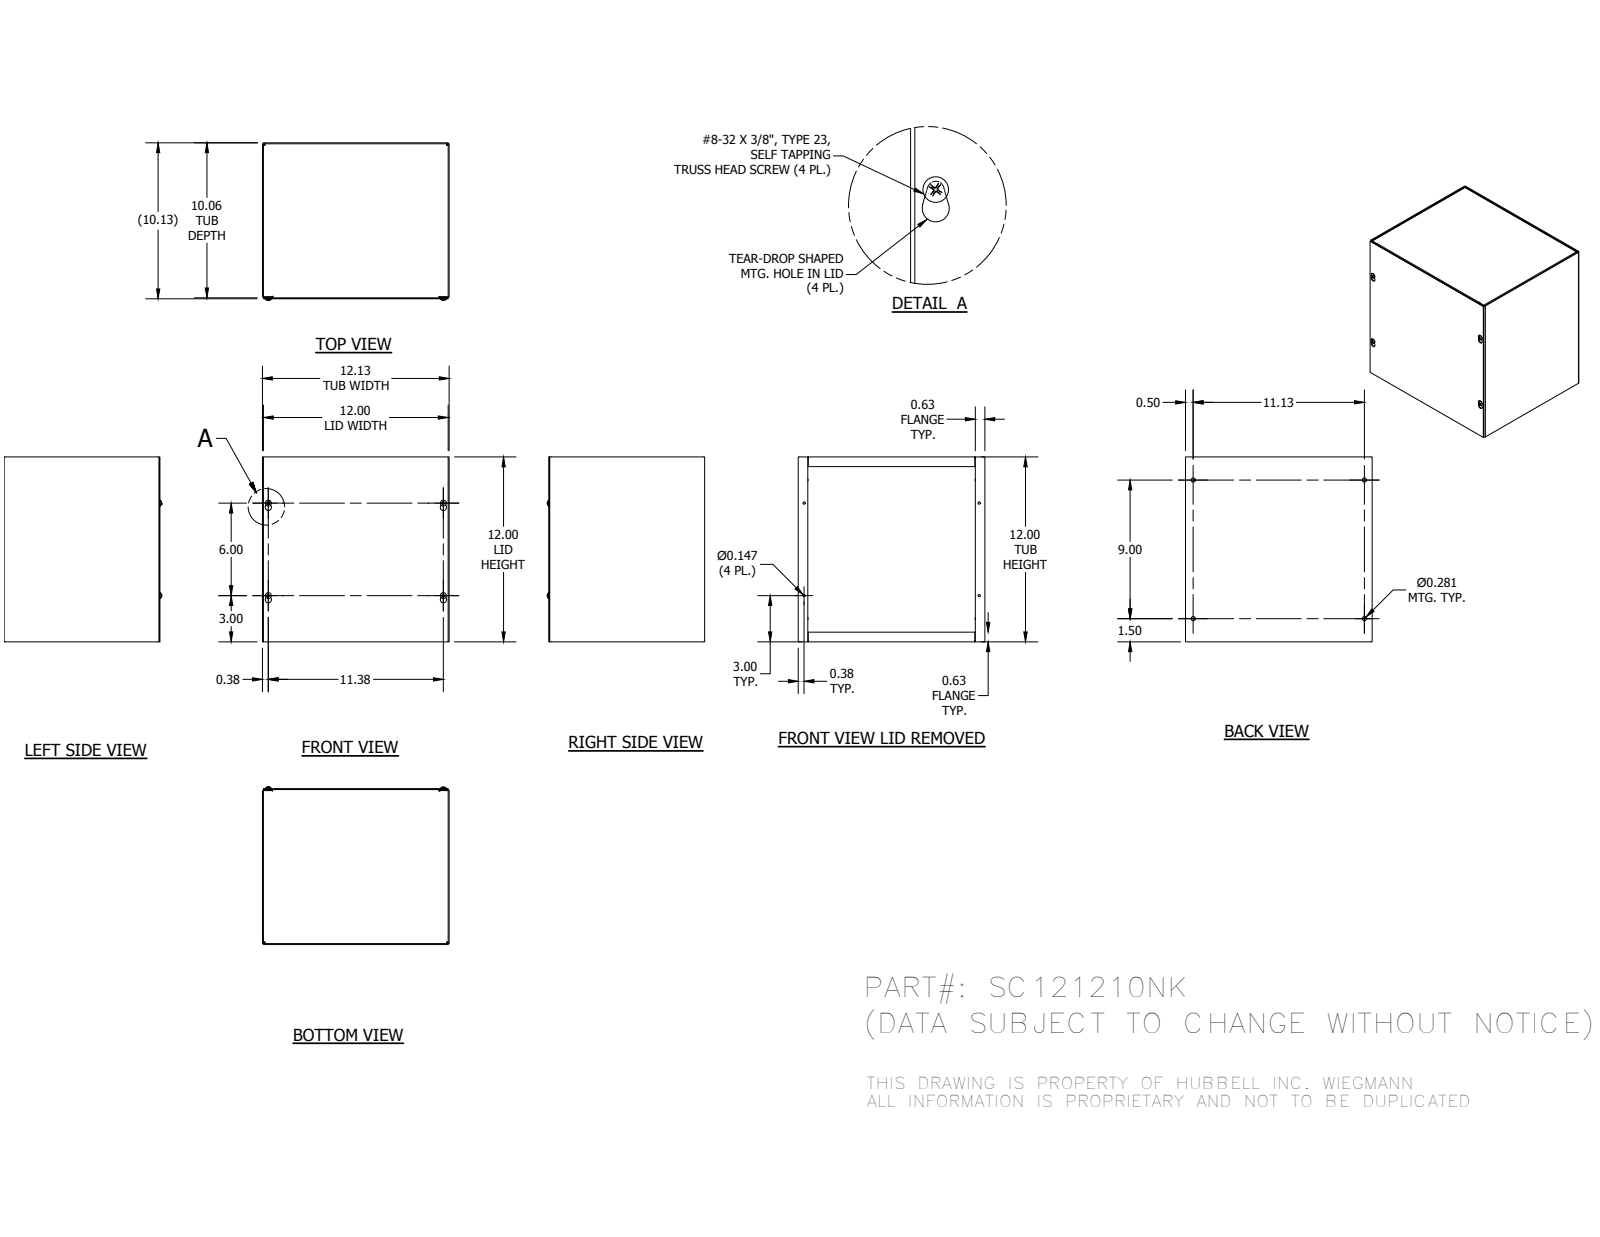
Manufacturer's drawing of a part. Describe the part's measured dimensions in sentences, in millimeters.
The part is named "SC121210NKBLR; SC1210NKTB; SC1212LPA; 34056 (+1 more)". Its 3-D file was written by "Autodesk Inventor 2014 (AUTOMOTIVE_DESIGN)". It is 8 solids with 268 faces: 152 planar, 48 cylindrical and 68 other. Overall it measures 307.98 by 304.8 by 259.72 millimeters. Its volume is 846 727 cubic millimeters and its surface area 1 077 000 square millimeters. Round holes: 4 of diameter 3.73, 4 of diameter 7.14. Round bosses or shafts: 4 of diameter 9.75, 4 of diameter 4.17. Partial cylindrical surfaces (rounded edges, fillets, slot ends): 12 of radius 0.79, 12 of radius 2.38, 4 of radius 3.17, 4 of radius 5.16. The main face-to-face distances are 1.59, 304.8, 303.21, 306.39, 254, 1.58, 255.59, 255.58, 257.17, 301.62. The hole center spacings are 38.23, 190.53, 288.28, 343.43, 152.4, 228.6, 282.58, 288.92.
